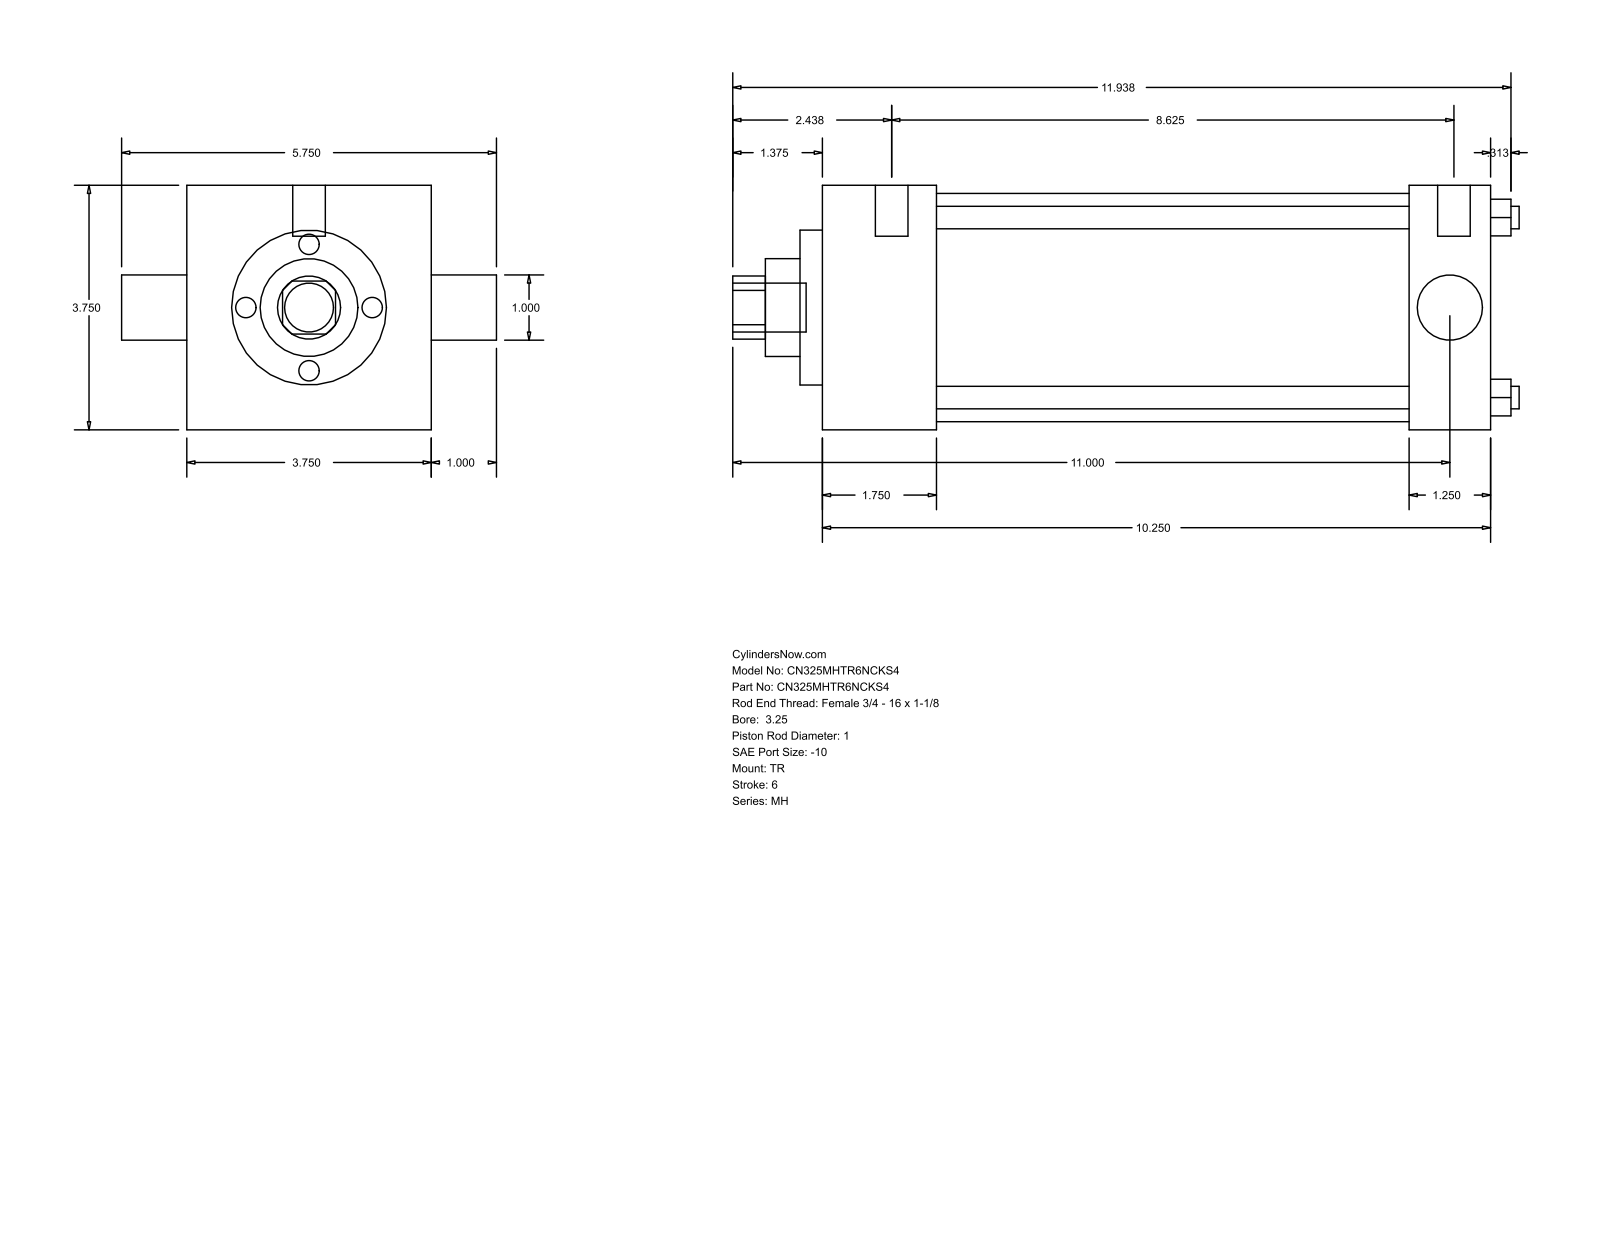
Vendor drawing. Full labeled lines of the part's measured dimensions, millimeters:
Part name (STEP PRODUCT): MH_TR__0325_1
STEP written by: GSSL Pune (CONFIG_CONTROL_DESIGN)
Units: millimetres
Bodies: 0 solids, 86 faces (61 planar, 25 cylindrical, 0 other)
Overall size (bounding box): 306.39 × 146.05 × 95.25
Round holes (diameter × count): ⌀8.76 ×4, ⌀25.4 ×2, ⌀38.1 ×1, ⌀60.33 ×1, ⌀88.9 ×1
Round bosses / shafts (diameter × count): ⌀5.56 ×3, ⌀12.7 ×2, ⌀19.05 ×1
Partial cylindrical surfaces — rounded edges, fillets, slot ends (radius × count): R12.29 ×1
Main face-to-face distances: 95.24, 260.35, 44.46, 228.6, 184.14, 215.89, 31.75, 8.73, 53.19, 237.33
Hole centre spacings: 49.57, 70.1, 99.14
